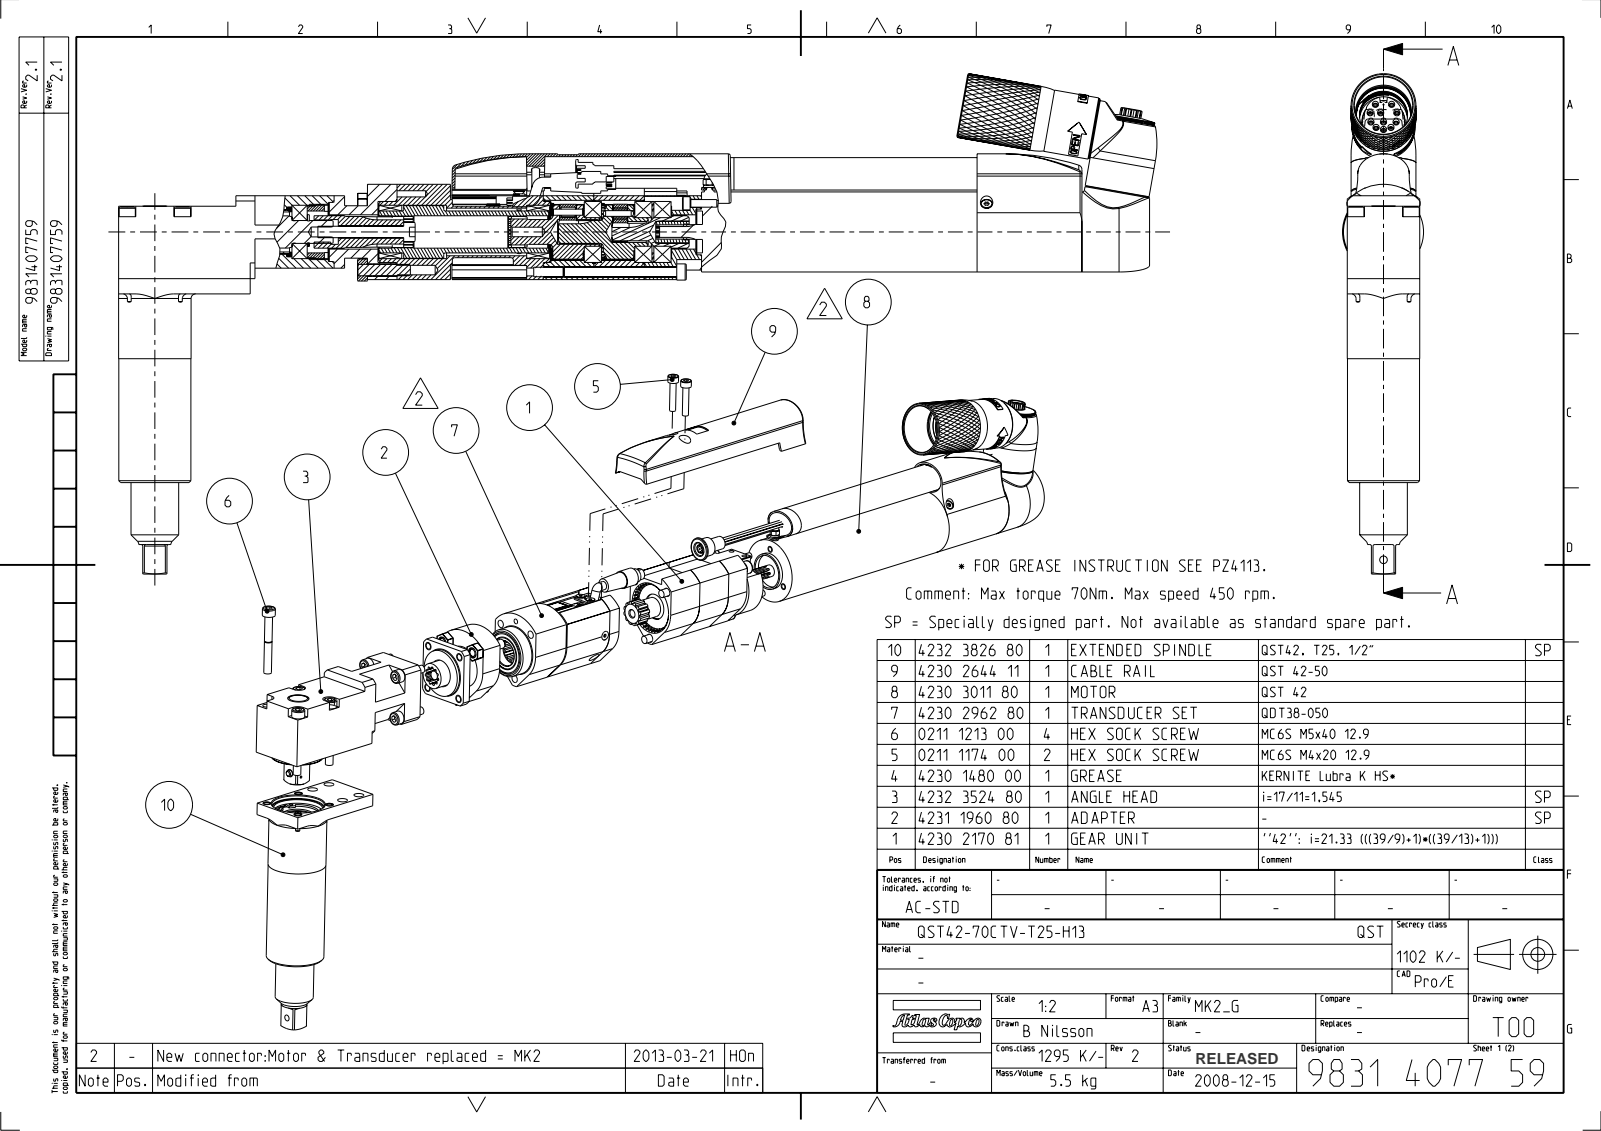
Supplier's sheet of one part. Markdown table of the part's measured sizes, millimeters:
| quantity | value |
| --- | --- |
| part name | 4230260102; 4230260112_ASM; 4230262500; 0219110017 (+8 more) |
| STEP written by | PRO/ENGINEER BY PARAMETRIC TECHNOLOGY CORPORATION, 2012420 (CONFIG_CONTROL_DESIGN) |
| units | millimeters |
| bodies | 50 solids, 4978 faces (1939 planar, 1636 cylindrical, 1403 other) |
| overall size | 544.51 × 262.56 × 42 |
| volume | 559 180 mm³ |
| surface area | 322 576 mm² |
| round holes (diameter × count) | 2.64 × 11, 3.27 × 11, 3.6 × 11, 5.5 × 11, 3.3 × 7, 5 × 7, 6.5 × 7, 2.46 × 5, 3.24 × 5, 4 × 5, 4.2 × 4, 6 × 4 |
| round bosses / shafts (diameter × count) | 5 × 12, 8.5 × 11, 6 × 7, 3 × 7, 34 × 5, 4 × 5, 2.5 × 3, 30 × 2 |
| partial cylindrical surfaces (radius × count) | 1 × 79, 0.1 × 53, 0.2 × 50, 0.5 × 17, 0.29 × 12, 0.51 × 12, 2 × 9, 0.8 × 6 |
| main face-to-face distances | 38, 5.5, 43.5, 8, 3, 32, 32.5, 26.5, 46, 305.7 |
| hole center spacings | 7.16, 29, 7.42, 15.92, 20.51, 15, 7.35, 7.41 |
